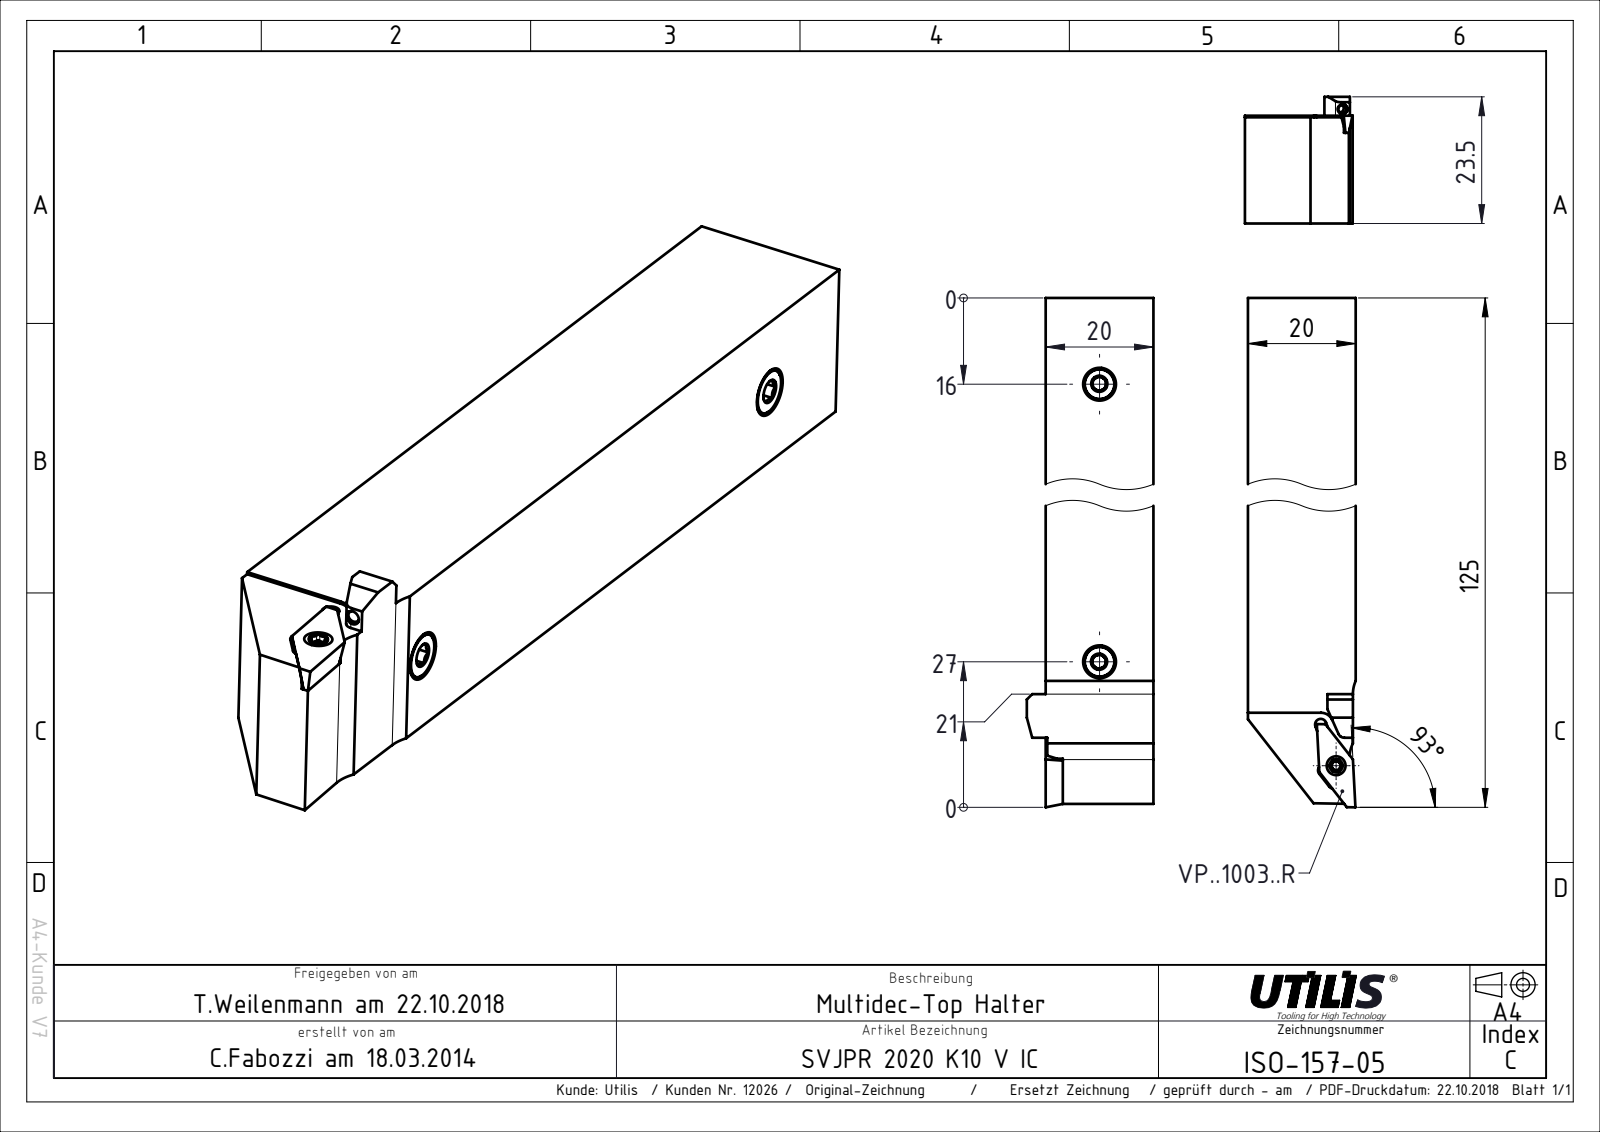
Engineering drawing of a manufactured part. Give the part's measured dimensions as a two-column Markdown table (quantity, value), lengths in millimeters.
| quantity | value |
| --- | --- |
| part name | ISO-157-05 |
| STEP written by | SolidWorks 2016 (AUTOMOTIVE_DESIGN) |
| units | millimeters |
| bodies | 1 solid, 51 faces (44 planar, 7 cylindrical, 0 other) |
| overall size | 125 × 23.5 × 20.2 |
| volume | 47 607 mm³ |
| surface area | 10 555 mm² |
| partial cylindrical surfaces (radius × count) | 1.05 × 3, 6.1 × 2, 2.3 × 1 |
| main face-to-face distances | 20, 19.73, 19.7, 23.5, 3.8, 3.5, 16.82, 2.88, 3.18, 6.68 |
